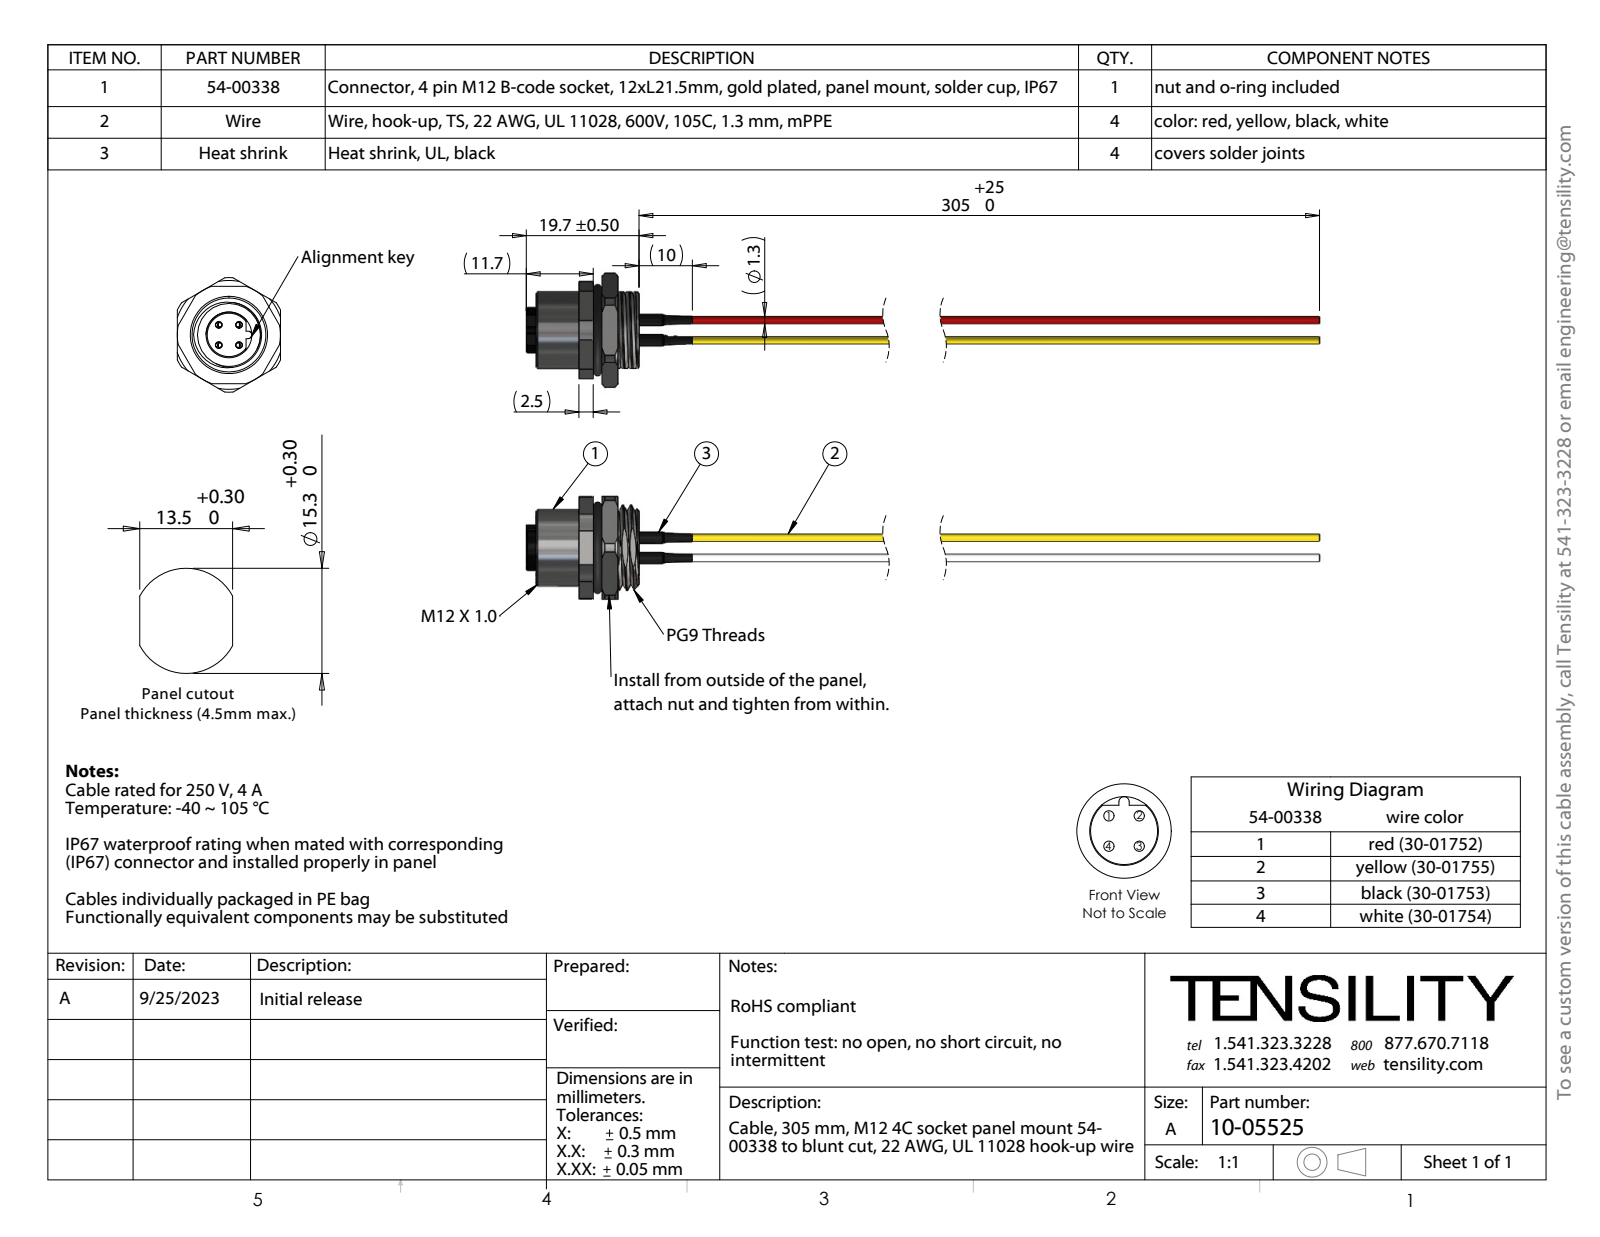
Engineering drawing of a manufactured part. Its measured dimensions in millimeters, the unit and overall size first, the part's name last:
Units: millimetres
Overall size (bounding box): 169 × 20 × 18
Round holes (diameter × count): ⌀1.1 ×4, ⌀1.2 ×4, ⌀9 ×1, ⌀11 ×1, ⌀14 ×1
Round bosses / shafts (diameter × count): ⌀2 ×4, ⌀1.6 ×4, ⌀1.5 ×4, ⌀1.3 ×4, ⌀13.5 ×1, ⌀13 ×1, ⌀12 ×1, ⌀10.6 ×1
Partial cylindrical surfaces — rounded edges, fillets, slot ends (radius × count): R0.1 ×8, R0.4 ×6, R0.65 ×1, R4 ×1, R7.5 ×1, R9 ×1, R10 ×1
Main face-to-face distances: 3, 7.3, 2.5, 2, 1.5, 5.3, 9.8, 5, 2.3, 18
Hole centre spacings: 0.32, 3.7, 3.53, 0.48, 3.37, 3.84, 0.37, 0.33
Volume: 3 682 mm³ · Surface area: 18 179 mm²
Bodies: 85 solids, 986 faces (306 planar, 479 cylindrical, 201 other)
Part name (STEP PRODUCT): 54-00338-03; 54-00338-04; 10-05525; 54-00338 (+8 more)
STEP written by: SolidWorks 2021 (AUTOMOTIVE_DESIGN)
